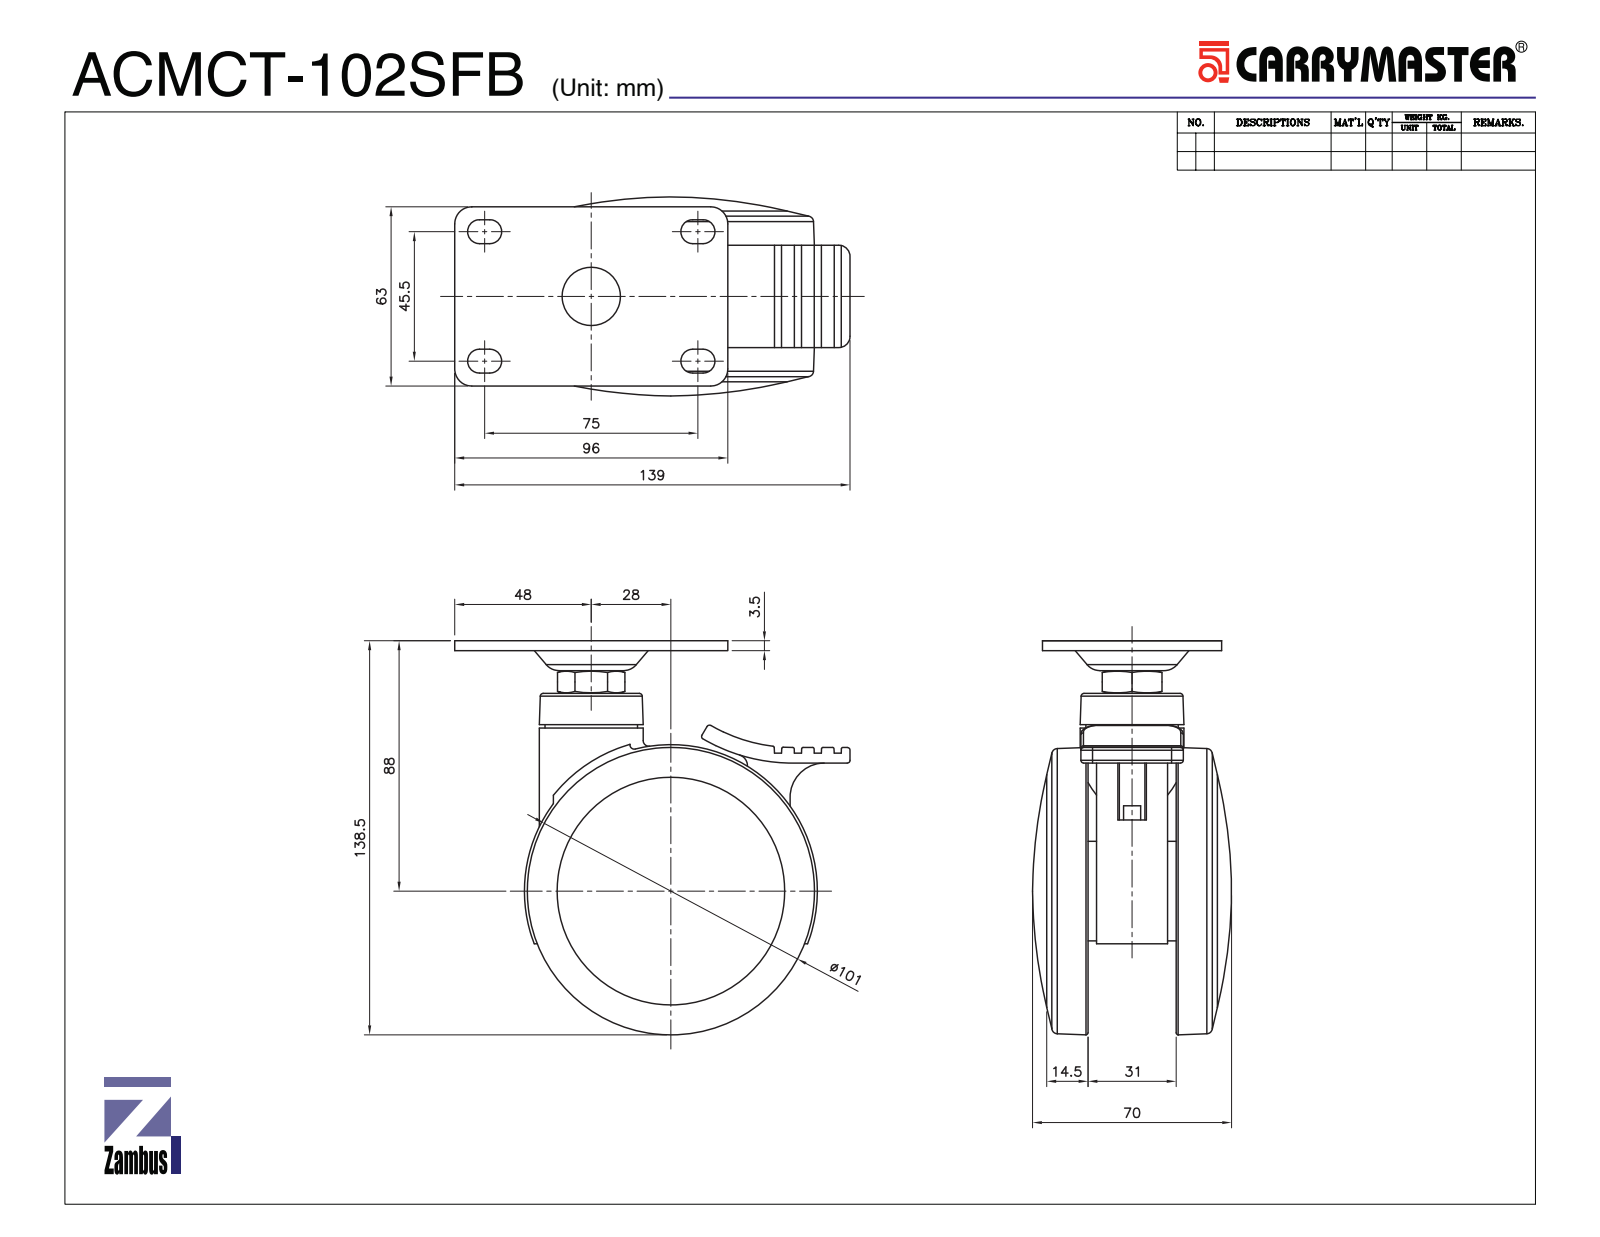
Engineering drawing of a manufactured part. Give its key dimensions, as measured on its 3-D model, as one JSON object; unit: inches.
{"part_name": "ACMC-102 WHEEL; 102 BRAKE TYPE FRAME; ACMCT-102 TOP PLATE; ACMCT-102SFB (+2 more)", "step_written_by": "SolidWorks 2019 (CONFIG_CONTROL_DESIGN)", "units": "inches", "bodies": {"solids": 6, "faces": 451, "planar": 141, "cylindrical": 208, "other": 102}, "overall_size": [5.472, 5.472, 2.756], "volume_in3": 23.88, "surface_area_in2": 151, "round_holes": [[0.984, 1], [2.835, 1], [3.157, 1]], "round_bosses_or_shafts": [[3.15, 1], [1.445, 1], [1.437, 1], [1.28, 1], [0.787, 1], [0.512, 1], [0.472, 1], [0.236, 1]], "partial_cylinders_radius": [[0.02, 72], [0.039, 9], [0.167, 8], [0.236, 4], [0.157, 3], [0.118, 2], [0.197, 2], [0.335, 1]], "face_to_face_distances": [0.118, 1.102, 1.496, 0.512, 0.394, 1.614, 0.984, 0.138, 1.22, 2.008]}
